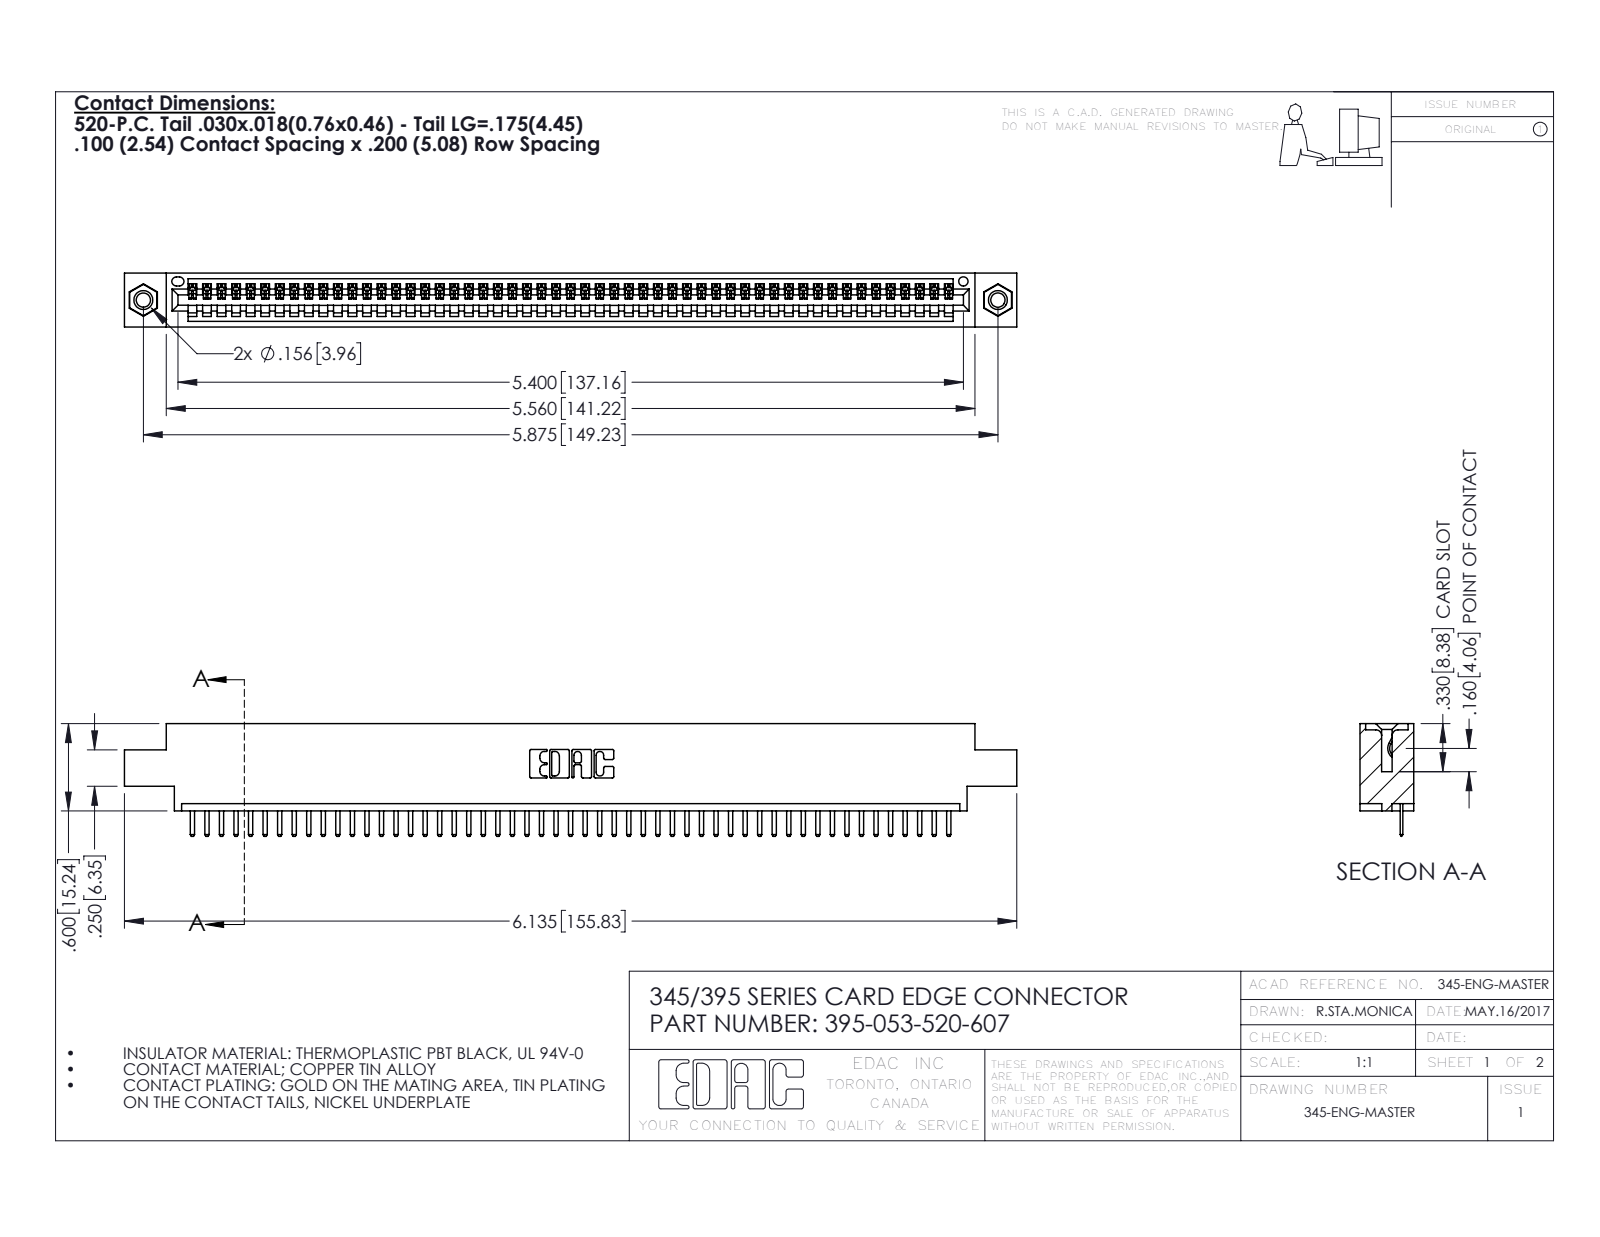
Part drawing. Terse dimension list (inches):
name: 345-292-001_345-293-120; 345-250-001_345-250-005-103; 345 Part_0.170 Offset - 0.156 Dia-TI; 395-053-520-607
written by: SolidWorks 2016 (CONFIG_CONTROL_DESIGN)
unit: in
bodies: 56 solids, 3476 faces (2342 planar, 1118 cylindrical, 16 other)
size: 6.135 × 0.775 × 0.37
volume: 0.892 in³; area: 29.8 in²
holes: 2× ⌀0.098, 2× ⌀0.125, 2× ⌀0.156, 1× ⌀0.064
bosses: 2× ⌀0.155
rounds: 108× R0.01, 106× R0.006, 22× R0.01, 6× R0.007, 6× R0.031, 3× R0.026, 2× R0.031, 2× R0.04
face distances: 0.072, 0.298, 0.37, 0.2, 0.098, 0.272, 0.025, 0.225, 0.072, 0.175
hole spacings: 0.27, 5.639, 5.875
